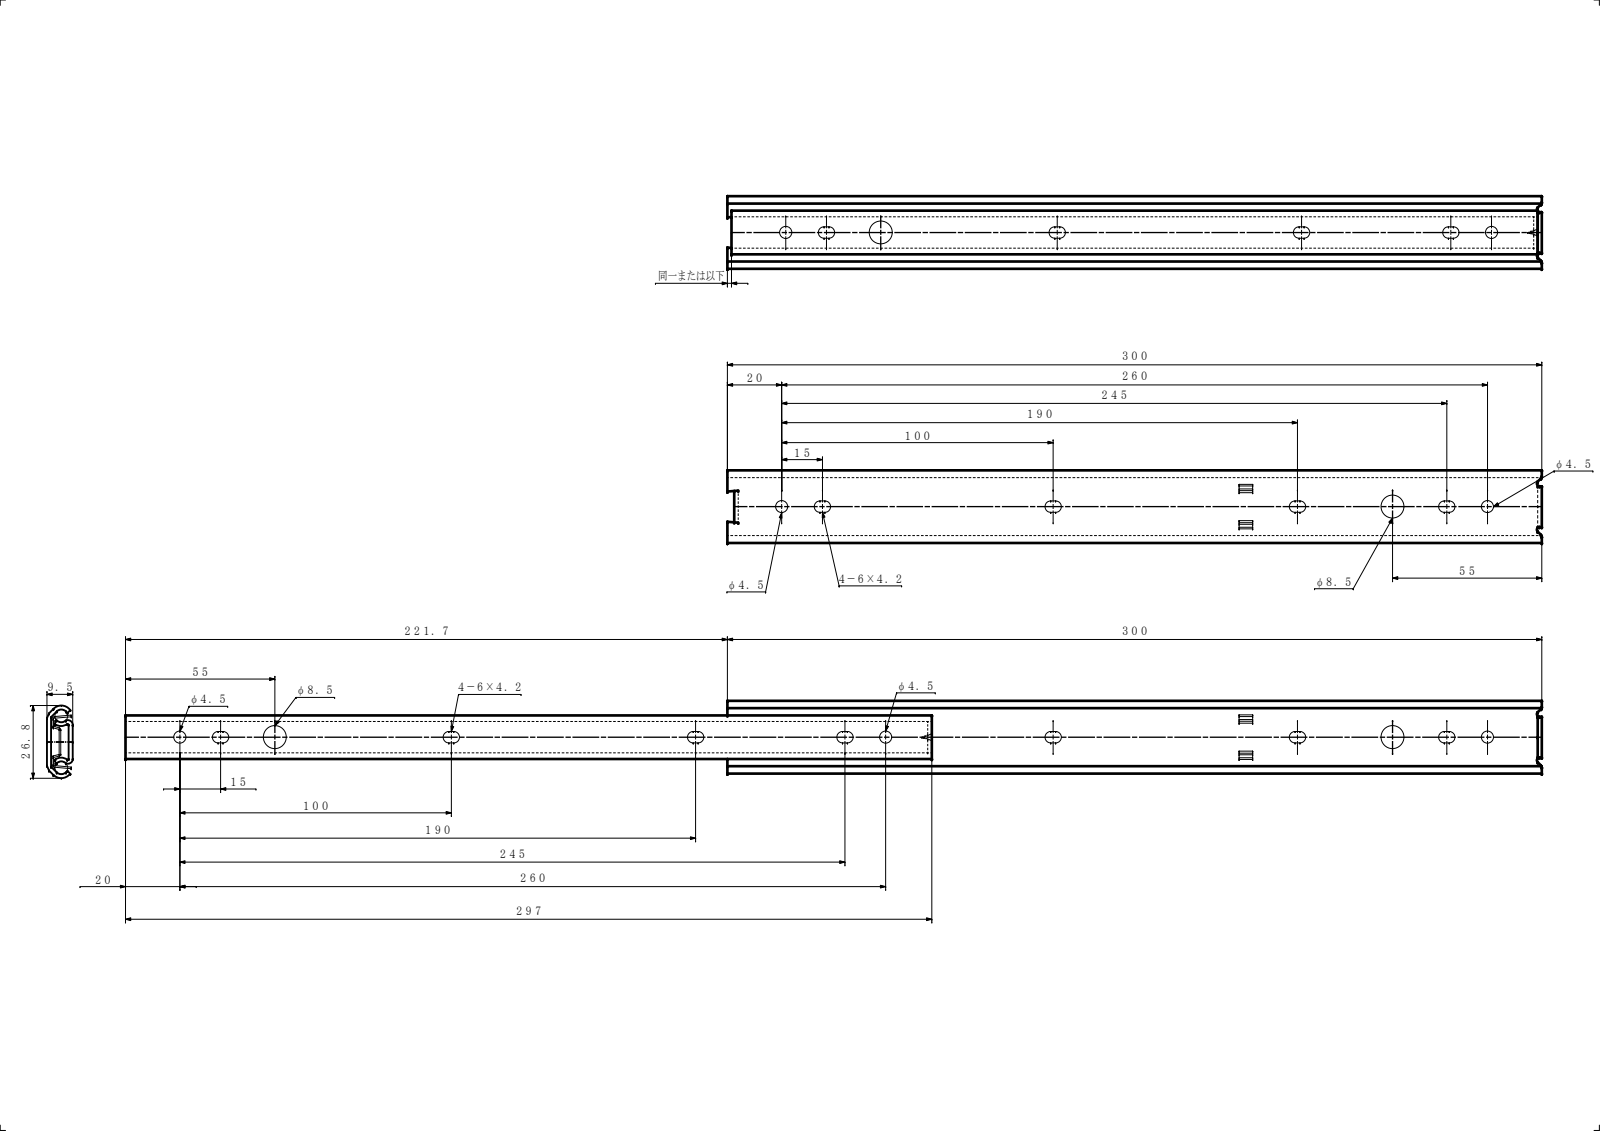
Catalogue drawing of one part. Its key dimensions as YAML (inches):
part_name: "U2721-300 IM; U2721-300 OM; U2721_300"
step_written_by: "SolidWorks 2019 (CONFIG_CONTROL_DESIGN)"
units: inches
bodies: {solids: 2, faces: 134, planar: 61, cylindrical: 73, other: 0}
overall_size: [20.539, 1.055, 0.378]
volume: 1.676
surface_area: 60.76
round_holes:
  - {diameter: 0.177, count: 4}
  - {diameter: 0.335, count: 2}
partial_cylinders:
  - {radius: 0.083, count: 16}
  - {radius: 0.079, count: 10}
  - {radius: 0.039, count: 5}
  - {radius: 0.02, count: 4}
  - {radius: 0.094, count: 4}
  - {radius: 0.153, count: 4}
  - {radius: 0.007, count: 2}
  - {radius: 0.051, count: 2}
face_to_face_distances: [0.059, 0.319, 0.378, 0.26, 8.846, 8.787, 11.654, 2.808, 8.906, 11.713]
hole_center_spacings: [1.378, 7.35, 8.728, 8.858, 10.236, 17.587, 1.508, 16.209]
